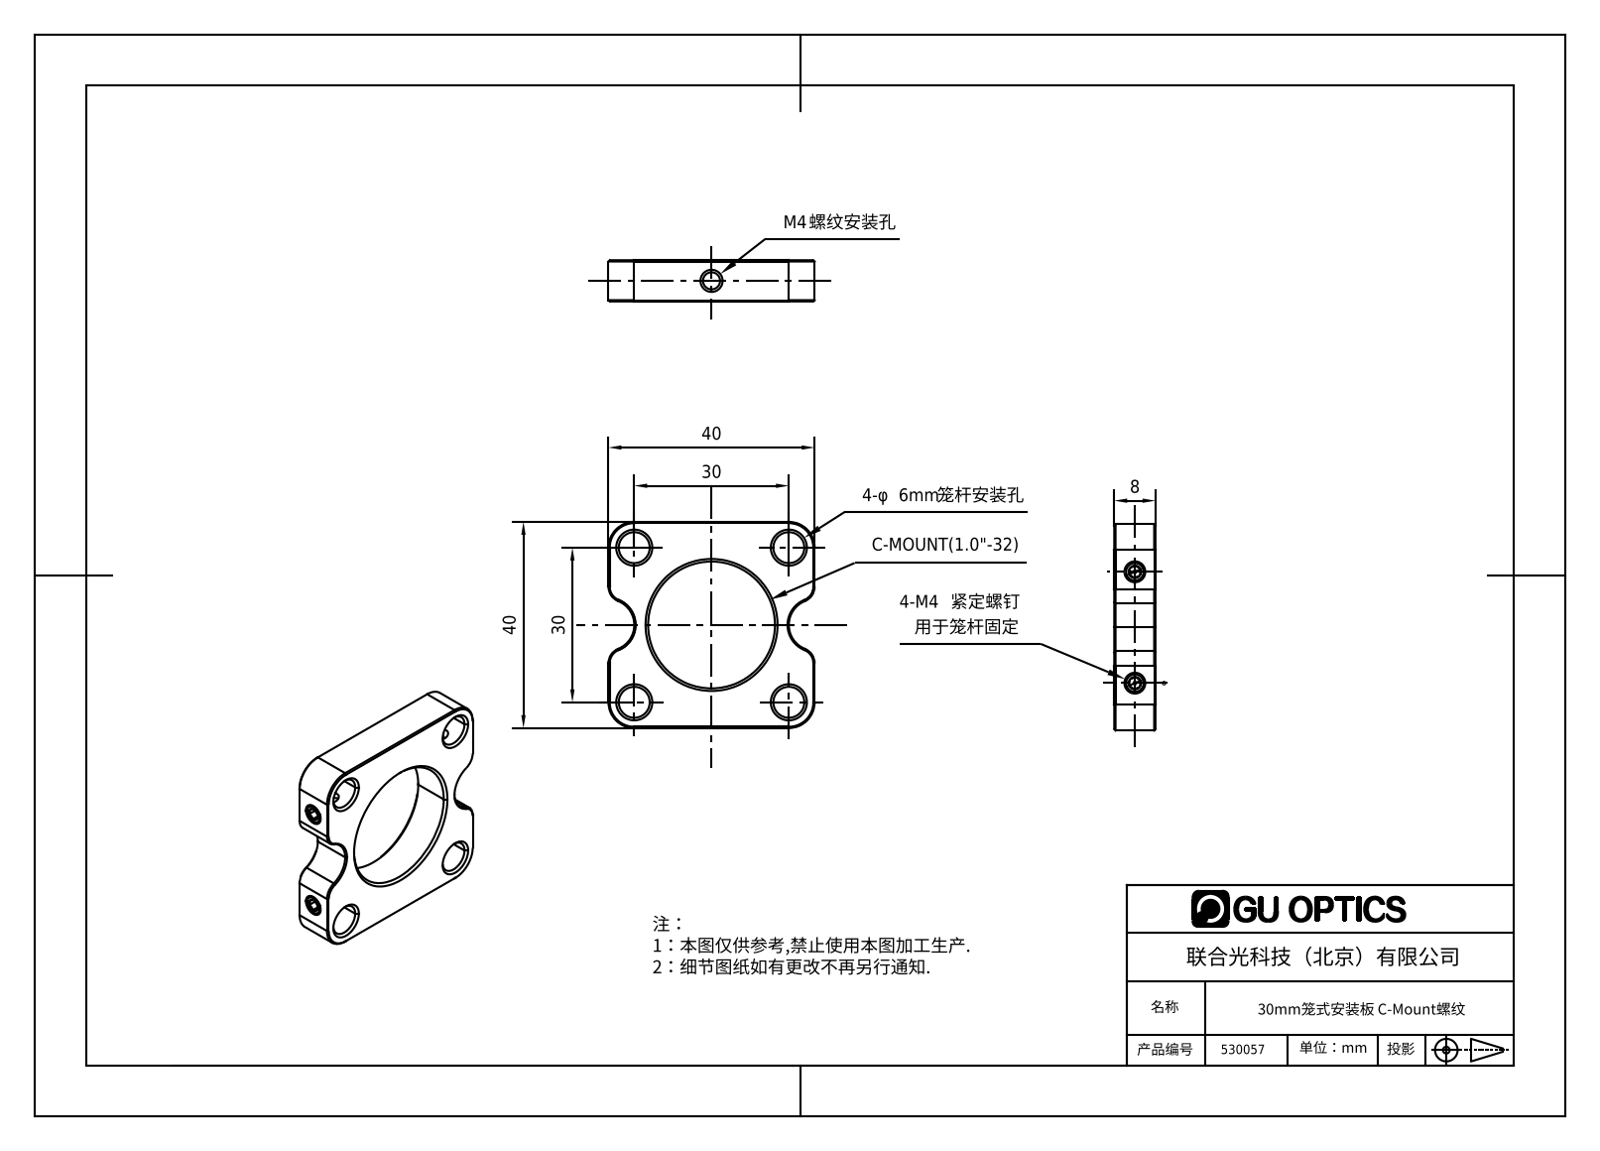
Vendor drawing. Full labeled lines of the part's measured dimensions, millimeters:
Part name (STEP PRODUCT): 2.2.1.17_L30B-C_30 mm笼板，带C-Mount螺纹，M4螺纹
STEP written by: SolidWorks 2018 (AUTOMOTIVE_DESIGN)
Units: millimetres
Bodies: 0 solids, 183 faces (52 planar, 31 cylindrical, 100 other)
Overall size (bounding box): 40 × 40 × 8
Round holes (diameter × count): ⌀6 ×4, ⌀3.3 ×3, ⌀24.61 ×1
Partial cylindrical surfaces — rounded edges, fillets, slot ends (radius × count): R5 ×6, R3 ×4
Main face-to-face distances: 8, 40, 33.58, 2.1, 17.15, 19.96, 2.8, 19.25, 15.05, 2.09
Hole centre spacings: 21.21, 30, 42.43, 21.6
